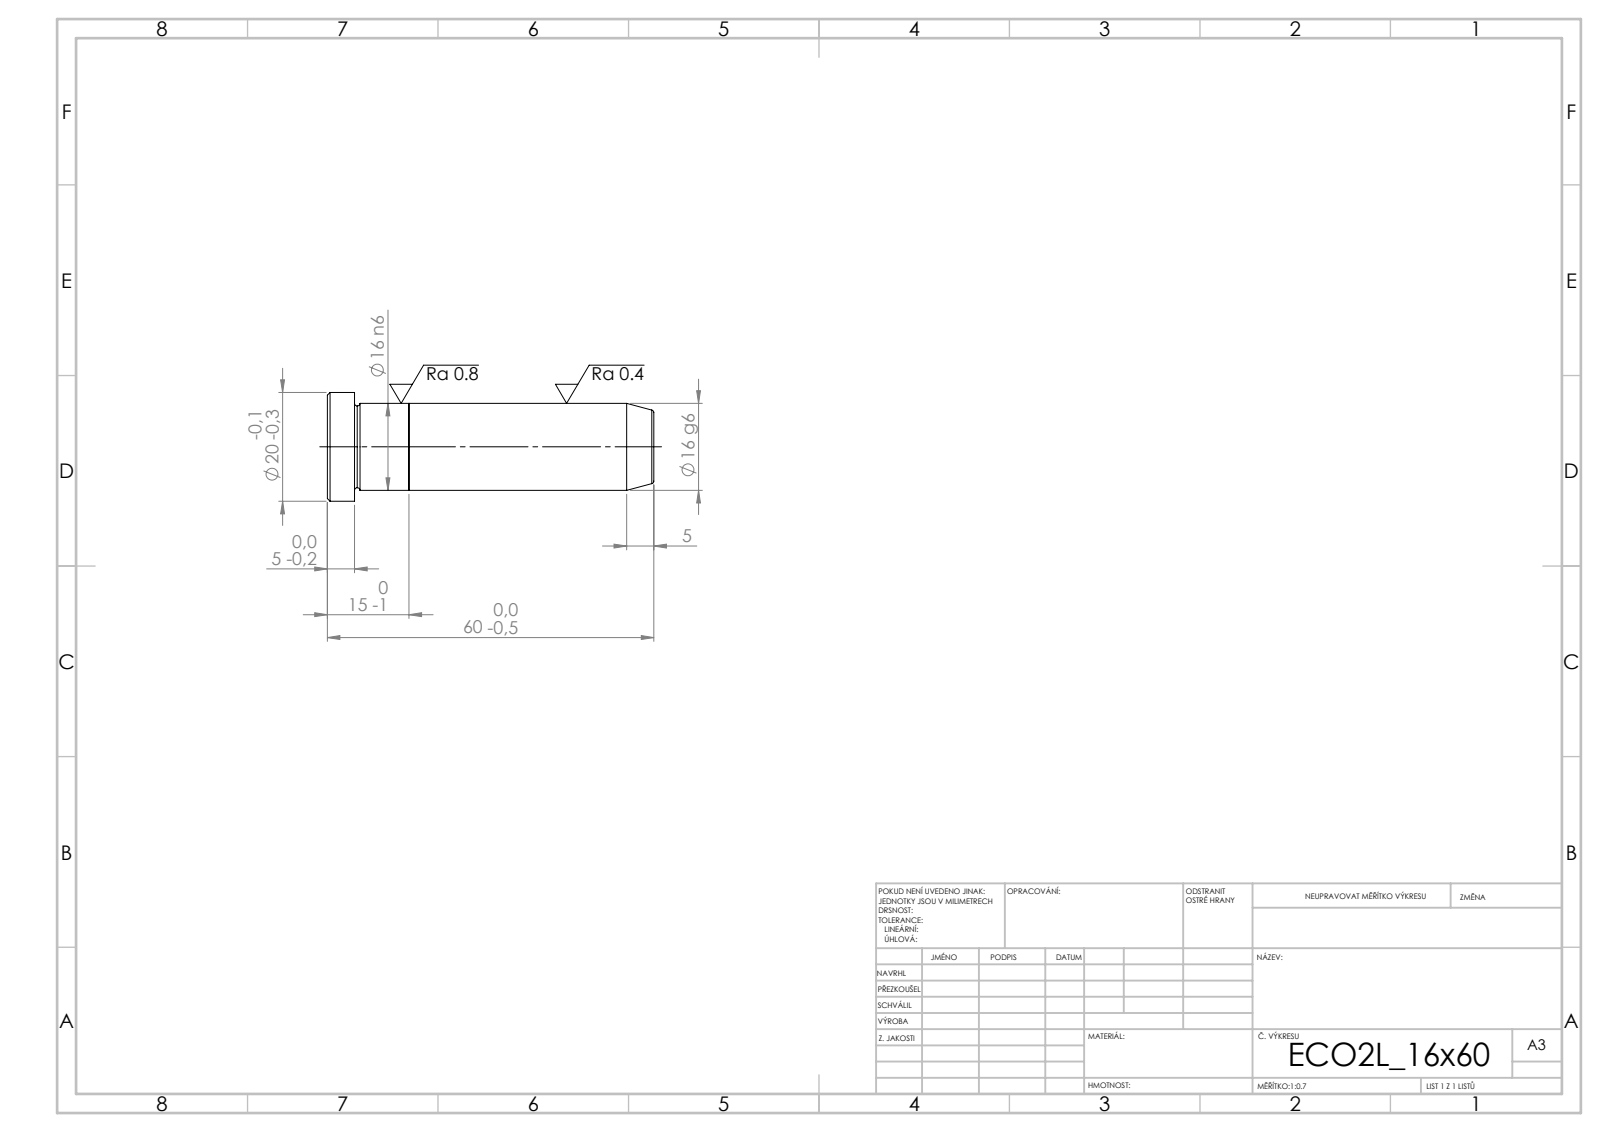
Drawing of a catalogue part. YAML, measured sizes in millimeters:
step_written_by: "SolidWorks 2019 (CONFIG_CONTROL_DESIGN)"
units: millimeters
bodies: {solids: 2, faces: 21, planar: 5, cylindrical: 6, other: 10}
overall_size: [60, 20, 20]
volume: 12442
surface_area: 4037
round_bosses_or_shafts:
  - {diameter: 20, count: 1}
  - {diameter: 16, count: 1}
face_to_face_distances: [15, 45, 60, 55, 10, 5]
